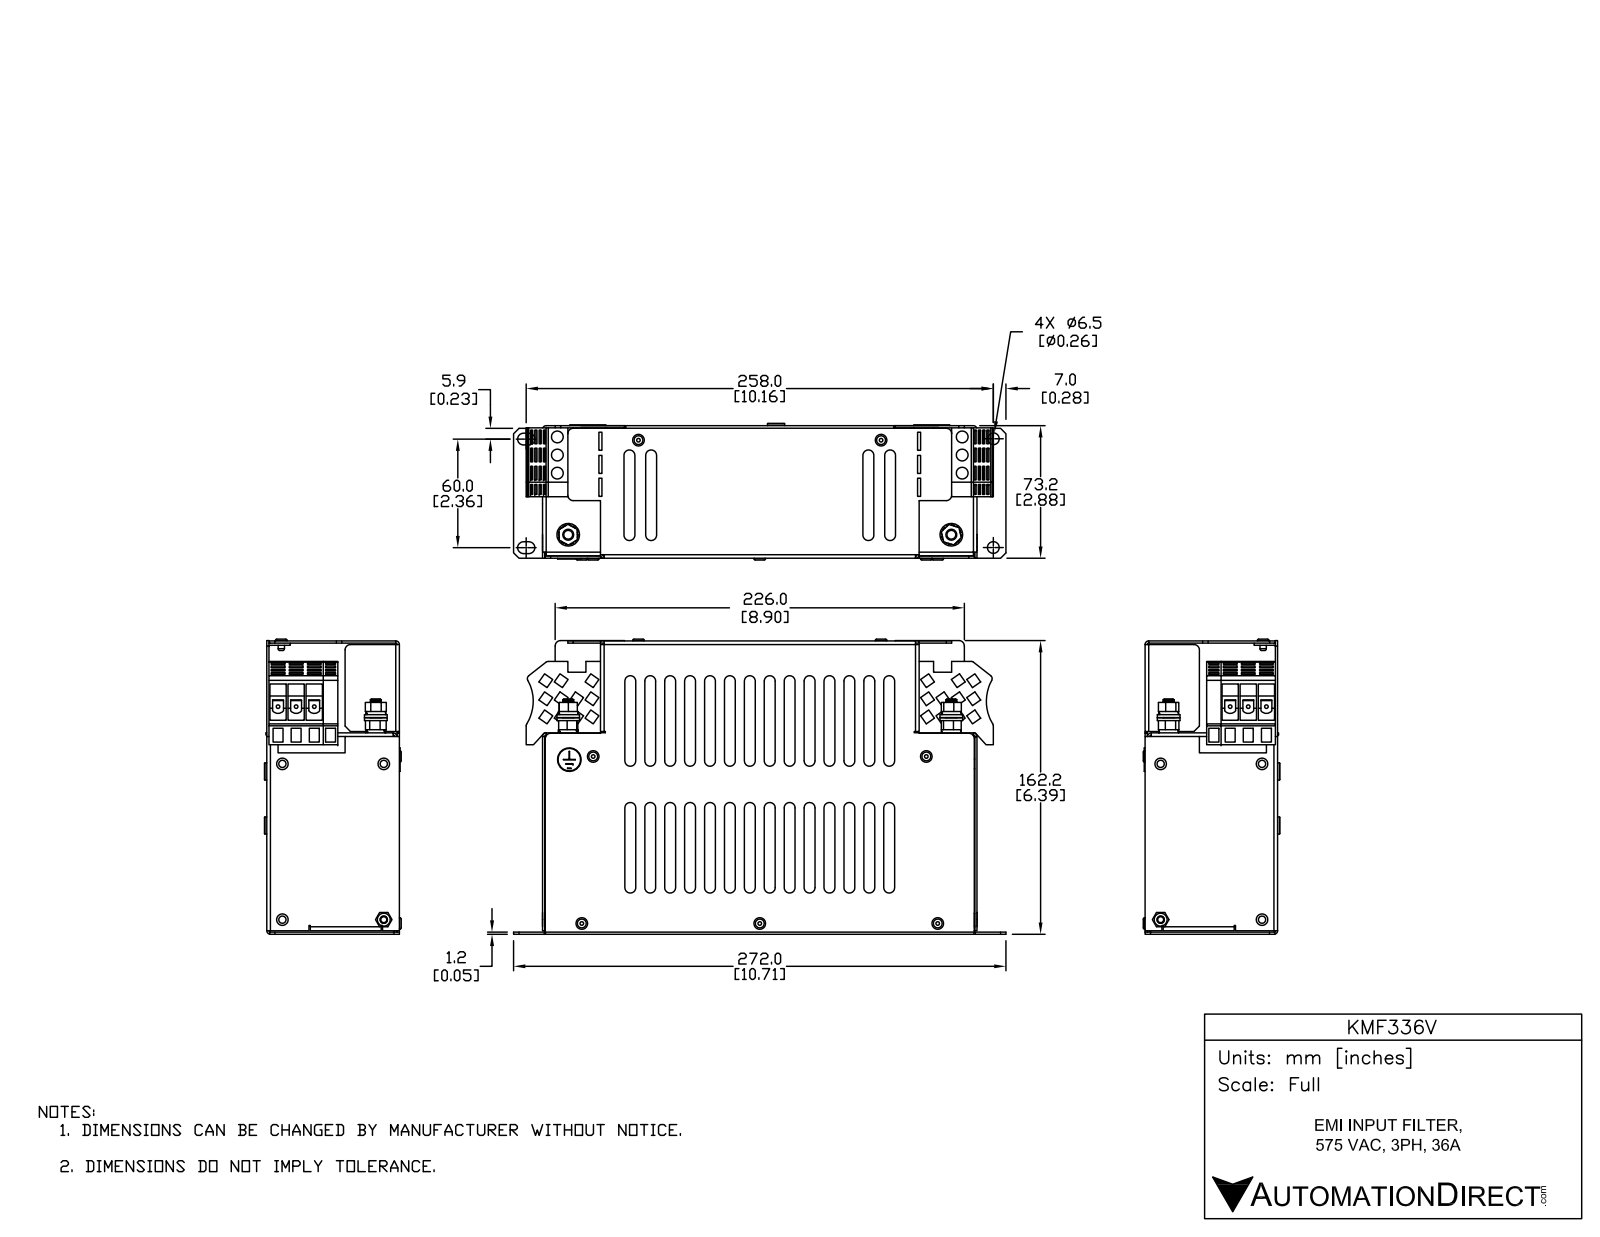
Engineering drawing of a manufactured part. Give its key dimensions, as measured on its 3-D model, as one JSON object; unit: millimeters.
{"part_name": "KMF336V", "step_written_by": "SolidWorks 2017 (AUTOMOTIVE_DESIGN)", "units": "millimeters", "bodies": {"solids": 37, "faces": 3108, "planar": 1966, "cylindrical": 738, "other": 404}, "overall_size": [272, 163, 75.5], "volume_mm3": 275500, "surface_area_mm2": 314600, "round_holes": [[6.5, 16], [3.3, 12], [3.5, 11], [6, 10], [2, 7], [4, 4], [4.5, 2], [5, 2], [4.8, 1], [7.1, 1]], "round_bosses_or_shafts": [[6.4, 3], [5.4, 3], [5.1, 3], [4.8, 3], [4.4, 3], [4.1, 3], [12.5, 2], [9.4, 2]], "partial_cylinders_radius": [[3, 75], [2, 22], [0.8, 10], [3.3, 4], [23.9, 4], [1, 3], [2.2, 3], [3.8, 3]], "face_to_face_distances": [1.2, 72, 70.8, 73.2, 160.8, 159.6, 238.8, 162, 110, 50.8], "hole_center_spacings": [10, 202.3, 202, 14.7, 14.8, 23.8, 203, 10.7]}
